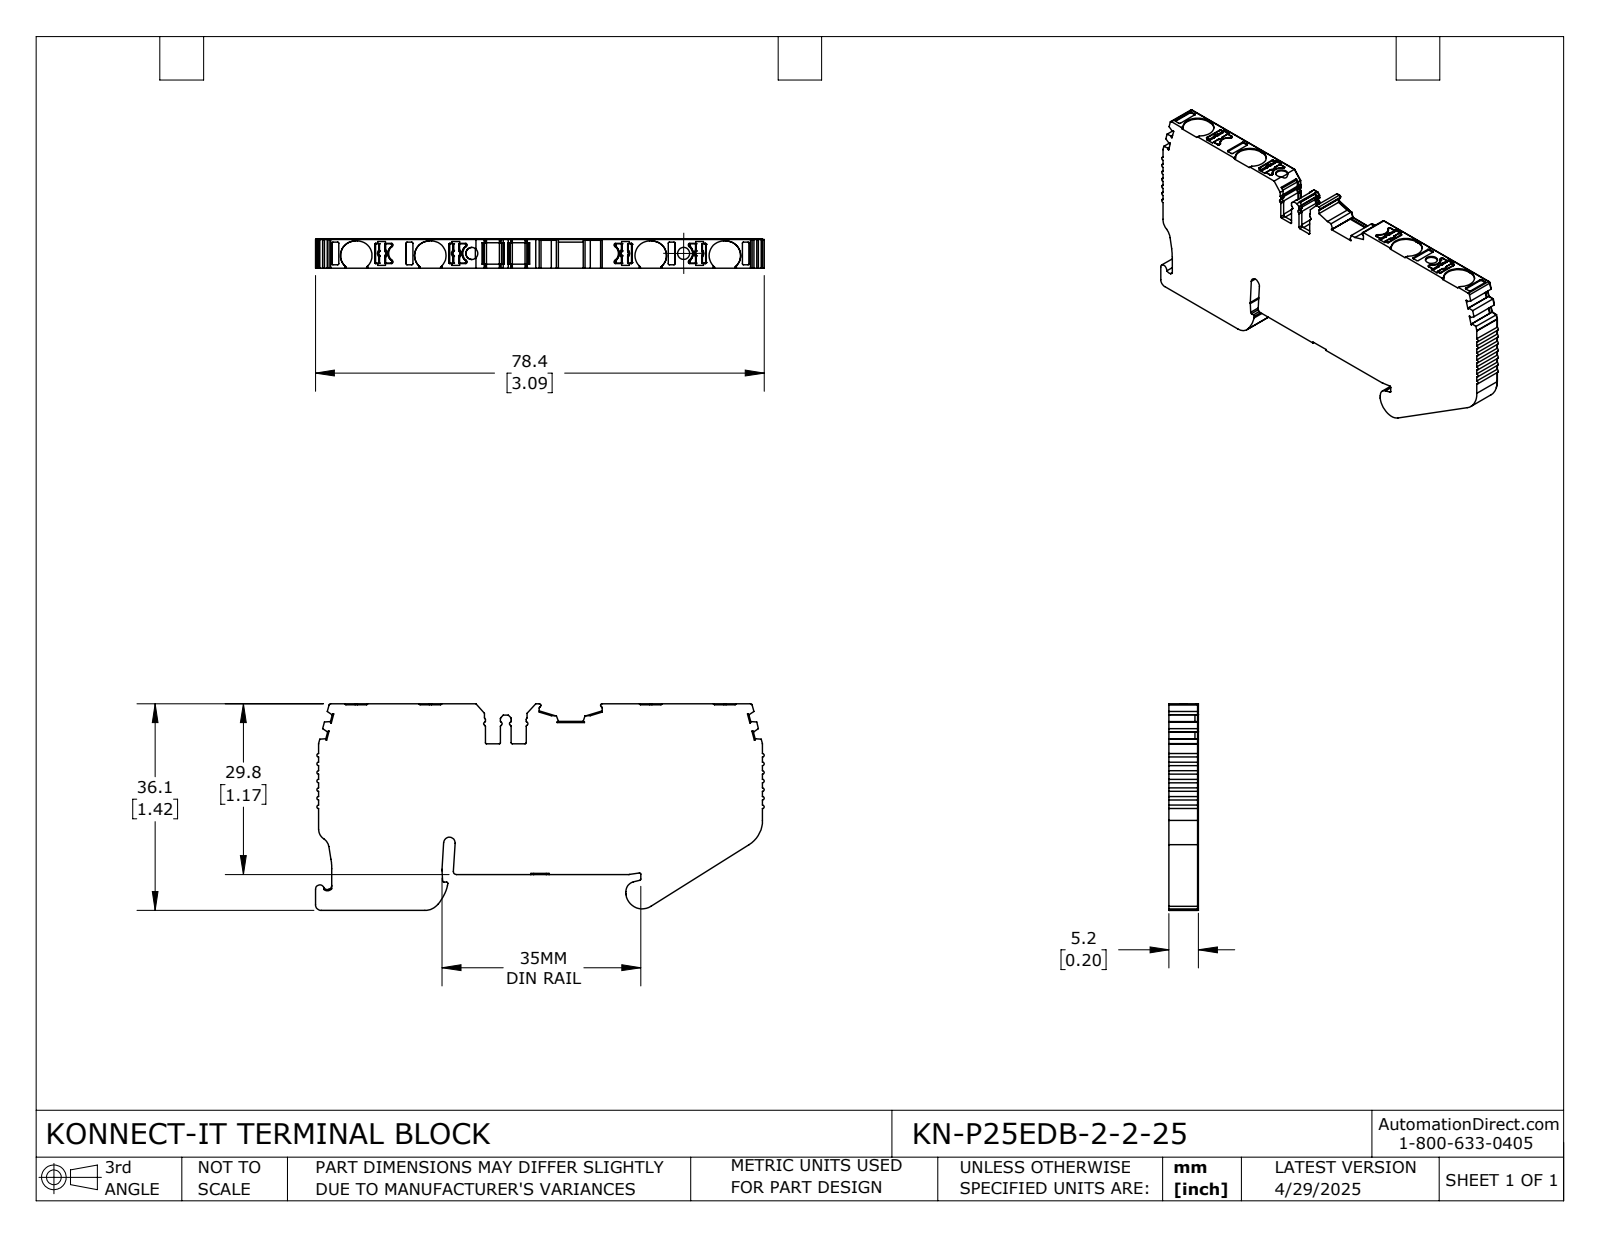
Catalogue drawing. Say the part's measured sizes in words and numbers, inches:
The part is named "KN-P25EDB-2-2-25". Its 3-D file was written by "SolidWorks 2024 (CONFIG_CONTROL_DESIGN)". It is 1 solid with 743 faces: 381 planar, 291 cylindrical and 71 other. Overall it measures 3.085 by 1.42 by 0.203 inches. Its volume is 0.731 cubic inches and its surface area 9.637 square inches. Round holes: 2 of diameter 0.083. Partial cylindrical surfaces (rounded edges, fillets, slot ends): 78 of radius 0.008, 39 of radius 0.012, 21 of radius 0.004, 18 of radius 0.02, 16 of radius 0.006, 9 of radius 0.016, 8 of radius 0.1, 4 of radius 0.059. The main face-to-face distances are 0.203, 1.166, 1.174, 0.246, 1.412, 1.42, 3.052, 0.047, 0.197, 0.177. The hole center spacings are 1.456.
